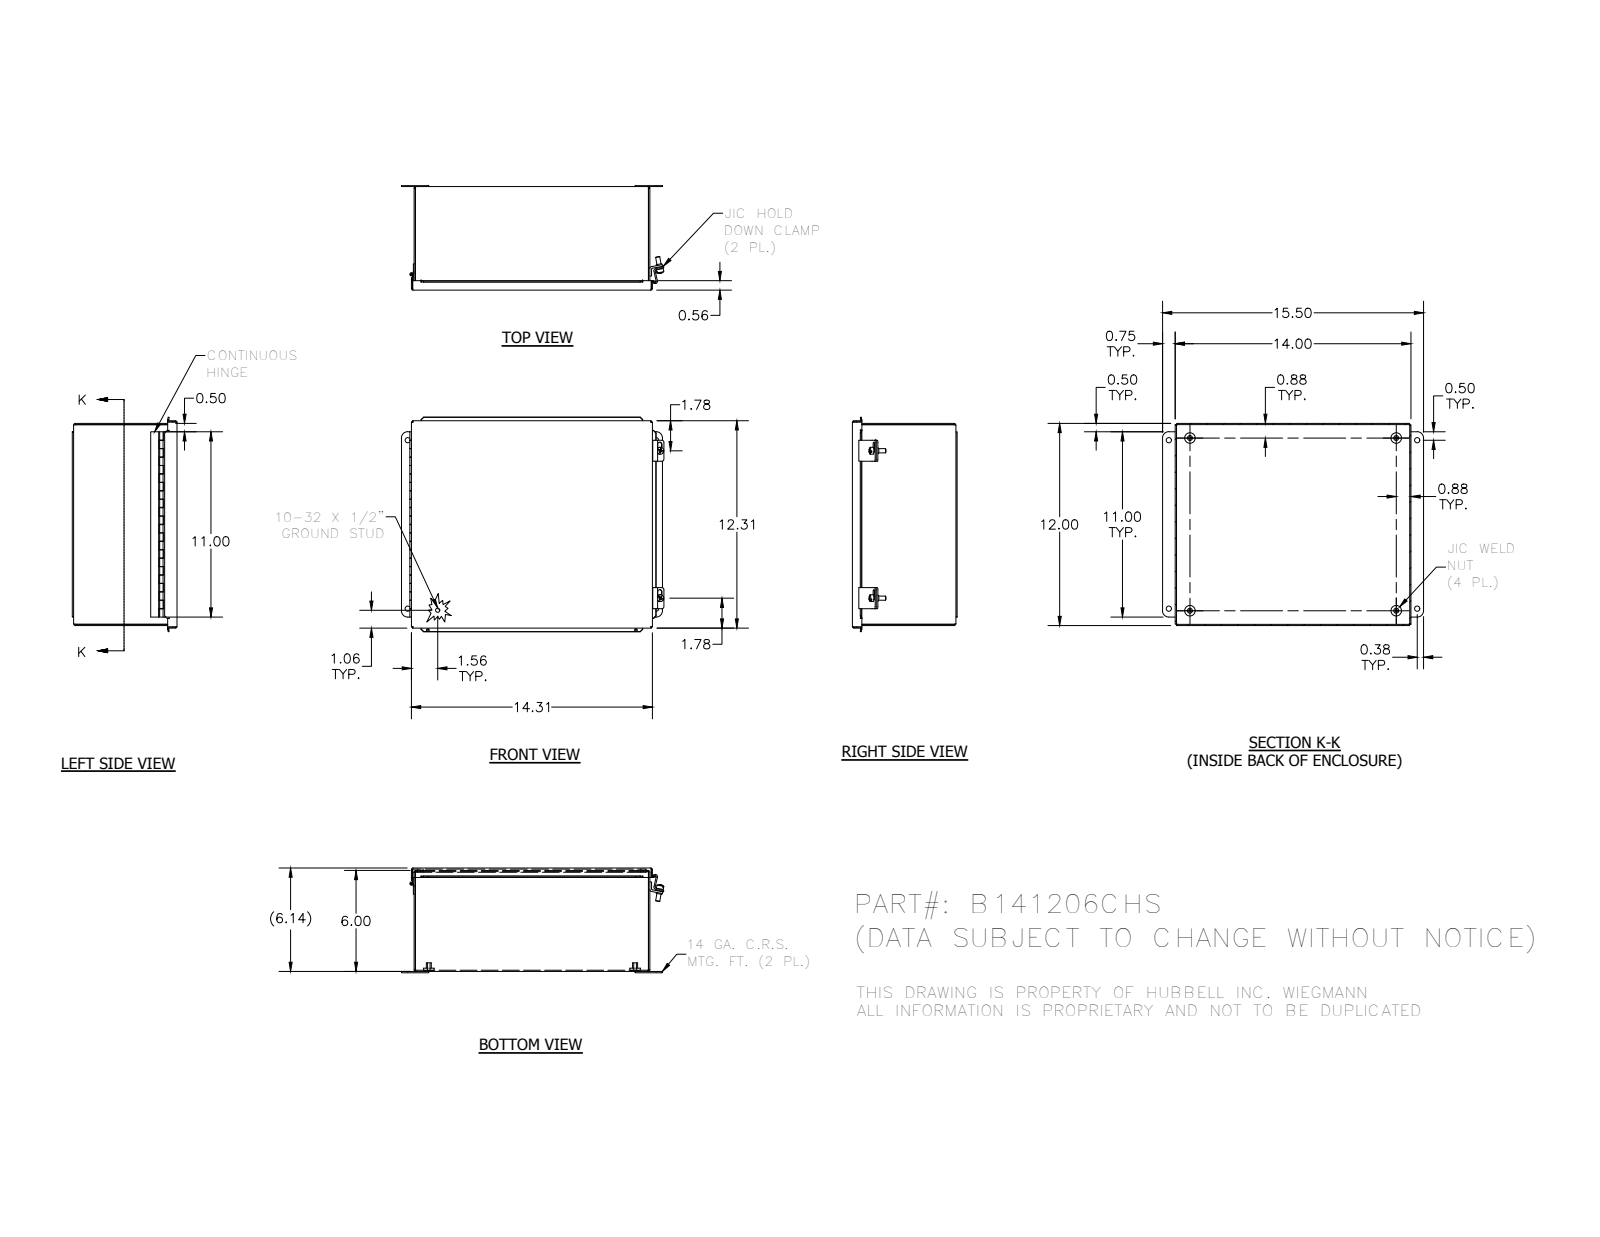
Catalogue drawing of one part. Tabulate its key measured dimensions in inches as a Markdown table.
| quantity | value |
| --- | --- |
| part name | B141206CHS; 3499; 3485; C1001 (+8 more) |
| STEP written by | Autodesk Inventor 2012 (AUTOMOTIVE_DESIGN) |
| units | inches |
| bodies | 20 solids, 499 faces (323 planar, 131 cylindrical, 45 other) |
| overall size | 15.585 × 12.739 × 6.219 |
| volume | 59.25 in³ |
| surface area | 1 625 in² |
| round holes (diameter × count) | 0.156 × 4, 0.31 × 4, 0.14 × 2, 0.196 × 2, 0.116 × 1 |
| round bosses / shafts (diameter × count) | 0.625 × 4, 0.3 × 4, 0.25 × 3, 0.41 × 2, 0.344 × 2, 0.2 × 1, 0.19 × 1, 0.1 × 1 |
| partial cylindrical surfaces (radius × count) | 0.031 × 15, 0.105 × 8, 0.125 × 8, 0.093 × 7, 0.133 × 4, 0.375 × 4, 0.063 × 3, 0.126 × 3 |
| main face-to-face distances | 0.074, 6.083, 0.062, 6.144, 6.009, 6.07, 11.926, 13.926, 12, 11.852 |
| hole center spacings | 1.256, 10.202, 13.5, 16.875, 10, 14.75, 17.82, 1.256 |
